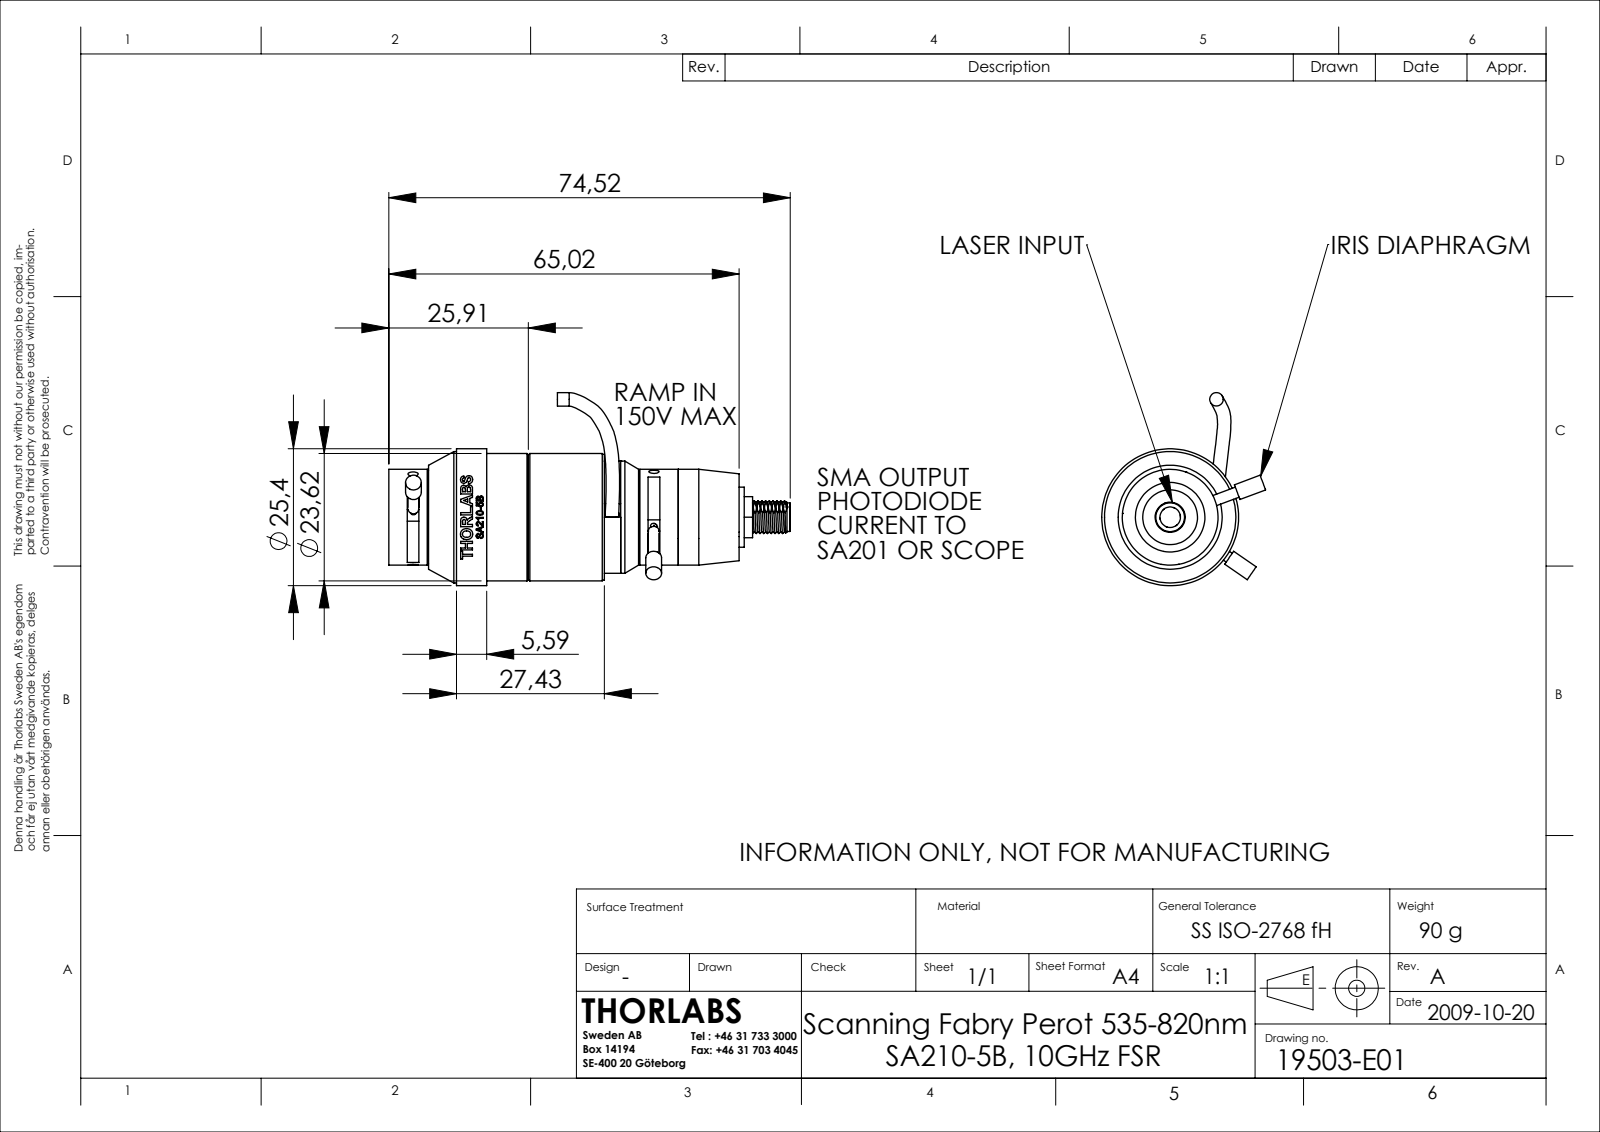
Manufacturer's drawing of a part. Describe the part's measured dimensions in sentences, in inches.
The part is named "6902-E0W; SM05PD1A-Diode Cover; kabel; 19503-E0W (+7 more)". Its 3-D file was written by "SolidWorks 2009 (CONFIG_CONTROL_DESIGN)". It is 9 solids with 415 faces: 160 planar, 180 cylindrical and 75 other. Overall it measures 2.934 by 1.41 by 1.197 inches. Its volume is 0.465 cubic inches and its surface area 22.59 square inches. Round holes: 10 of diameter 0.058, 6 of diameter 0.075, 1 of diameter 0.039, 1 of diameter 0.106, 1 of diameter 0.15, 1 of diameter 0.181, 1 of diameter 0.22, 1 of diameter 0.24, 1 of diameter 0.25, 1 of diameter 0.325, 1 of diameter 0.385, 1 of diameter 0.395. Round bosses or shafts: 2 of diameter 0.115, 2 of diameter 0.078, 1 of diameter 1, 1 of diameter 0.96, 1 of diameter 0.93, 1 of diameter 0.92, 1 of diameter 0.906, 1 of diameter 0.82. Partial cylindrical surfaces (rounded edges, fillets, slot ends): 1 of radius 0.014, 1 of radius 0.02, 1 of radius 0.055, 1 of radius 0.063, 1 of radius 0.075, 1 of radius 0.11, 1 of radius 0.125, 1 of radius 0.282. The main face-to-face distances are 0.29, 0.1, 1.725, 0.15, 1.825, 0.08, 0.13, 1.285, 1.575, 0.44. The hole center spacings are 0.148, 0.257, 0.297, 0.137, 0.263, 0.013, 0.16, 0.25.
